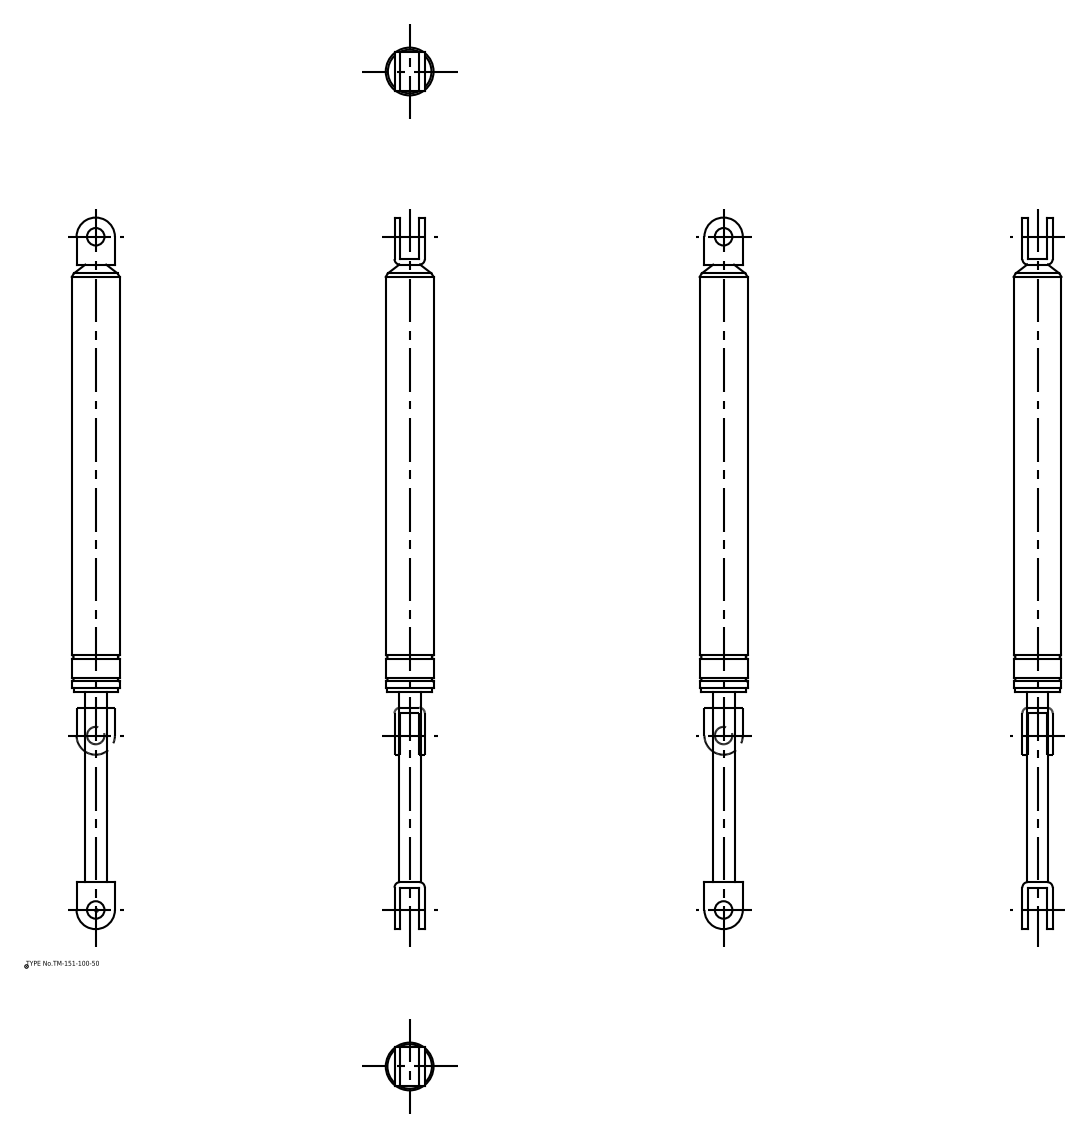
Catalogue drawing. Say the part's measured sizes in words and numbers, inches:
The part is named "TM_151_100_50; TM_151_100_50_div". Its 3-D file was written by "spGate 16.7.1 (AUTOMOTIVE_DESIGN)". It is 2 solids with 64 faces: 22 planar, 32 cylindrical and 10 other. Overall it measures 16.063 by 1.11 by 1.11 inches. Its volume is 9.98 cubic inches and its surface area 49.84 square inches. Round holes: 2 of diameter 0.394. Round bosses or shafts: 1 of diameter 1.11, 1 of diameter 1.079, 1 of diameter 1.004, 1 of diameter 0.492. Partial cylindrical surfaces (rounded edges, fillets, slot ends): 4 of radius 0.126, 2 of radius 0.433. The main face-to-face distances are 0.126, 0.559, 0.685, 0.433, 0.866, 14.063, 4.417, 14.189, 9.772, 9.646. The hole center spacings are 15.197.
